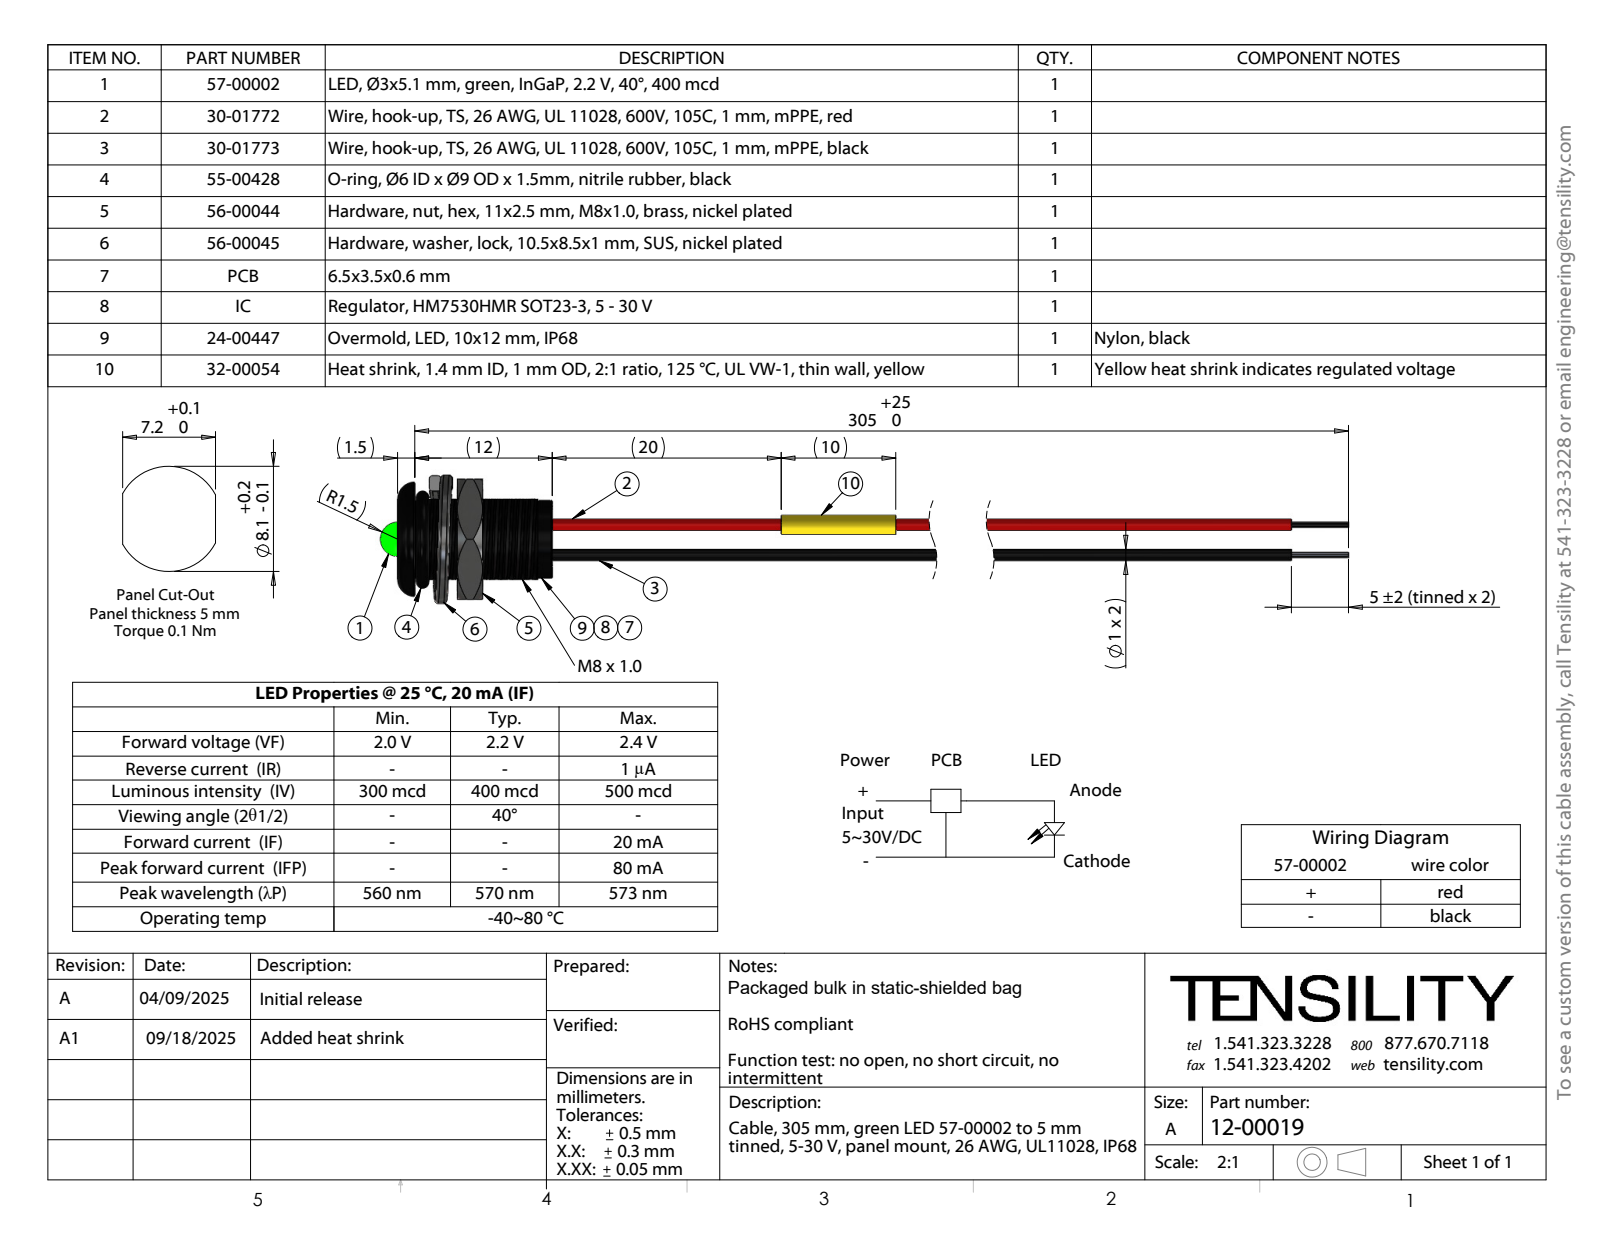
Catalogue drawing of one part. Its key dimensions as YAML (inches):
part_name: "30-01773_stripped and tinned; 56-00044; 57-00002_trimmed leads; 55-00428 (+4 more)"
step_written_by: "SolidWorks 2021 (CONFIG_CONTROL_DESIGN)"
units: inches
bodies: {solids: 57, faces: 555, planar: 186, cylindrical: 246, other: 123}
overall_size: [6.693, 0.477, 0.441]
volume: 0.061
surface_area: 9.157
round_holes:
  - {diameter: 0.039, count: 2}
round_bosses_or_shafts:
  - {diameter: 0.039, count: 2}
  - {diameter: 0.02, count: 2}
  - {diameter: 0.268, count: 1}
  - {diameter: 0.118, count: 1}
partial_cylinders:
  - {radius: 0.137, count: 1}
  - {radius: 0.157, count: 1}
face_to_face_distances: [0.059, 0.531, 0.472, 0.413, 0.205, 0.146, 0.326, 0.292, 0.233, 0.087]
hole_center_spacings: [0.014, 0.015, 0.013, 0.098, 0.099, 0.096, 0.096, 0.101]
